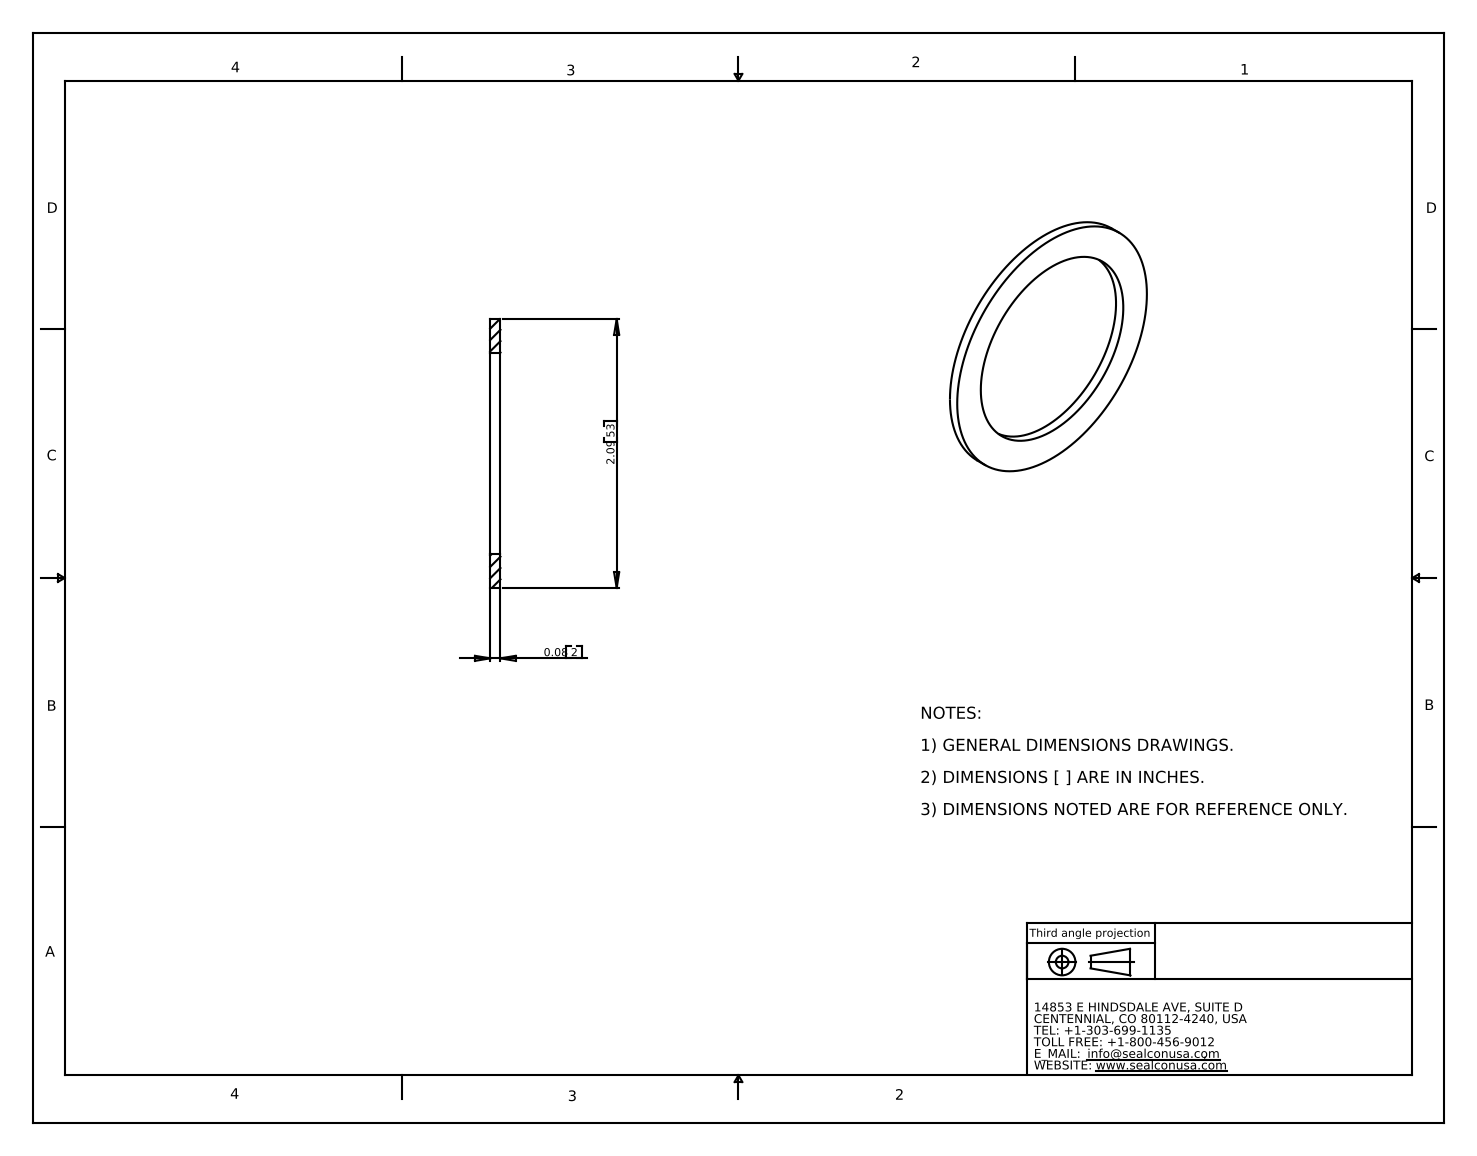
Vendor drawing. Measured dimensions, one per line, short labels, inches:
name: SM-40-VT
written by: SolidWorks 2007 (CONFIG_CONTROL_DESIGN)
unit: in
bodies: 1 solid, 6 faces (2 planar, 4 cylindrical, 0 other)
size: 2.09 × 2.09 × 0.08
volume: 0.12 in³; area: 3.909 in²
holes: 1× ⌀1.57
bosses: 1× ⌀2.09
face distances: 0.08
